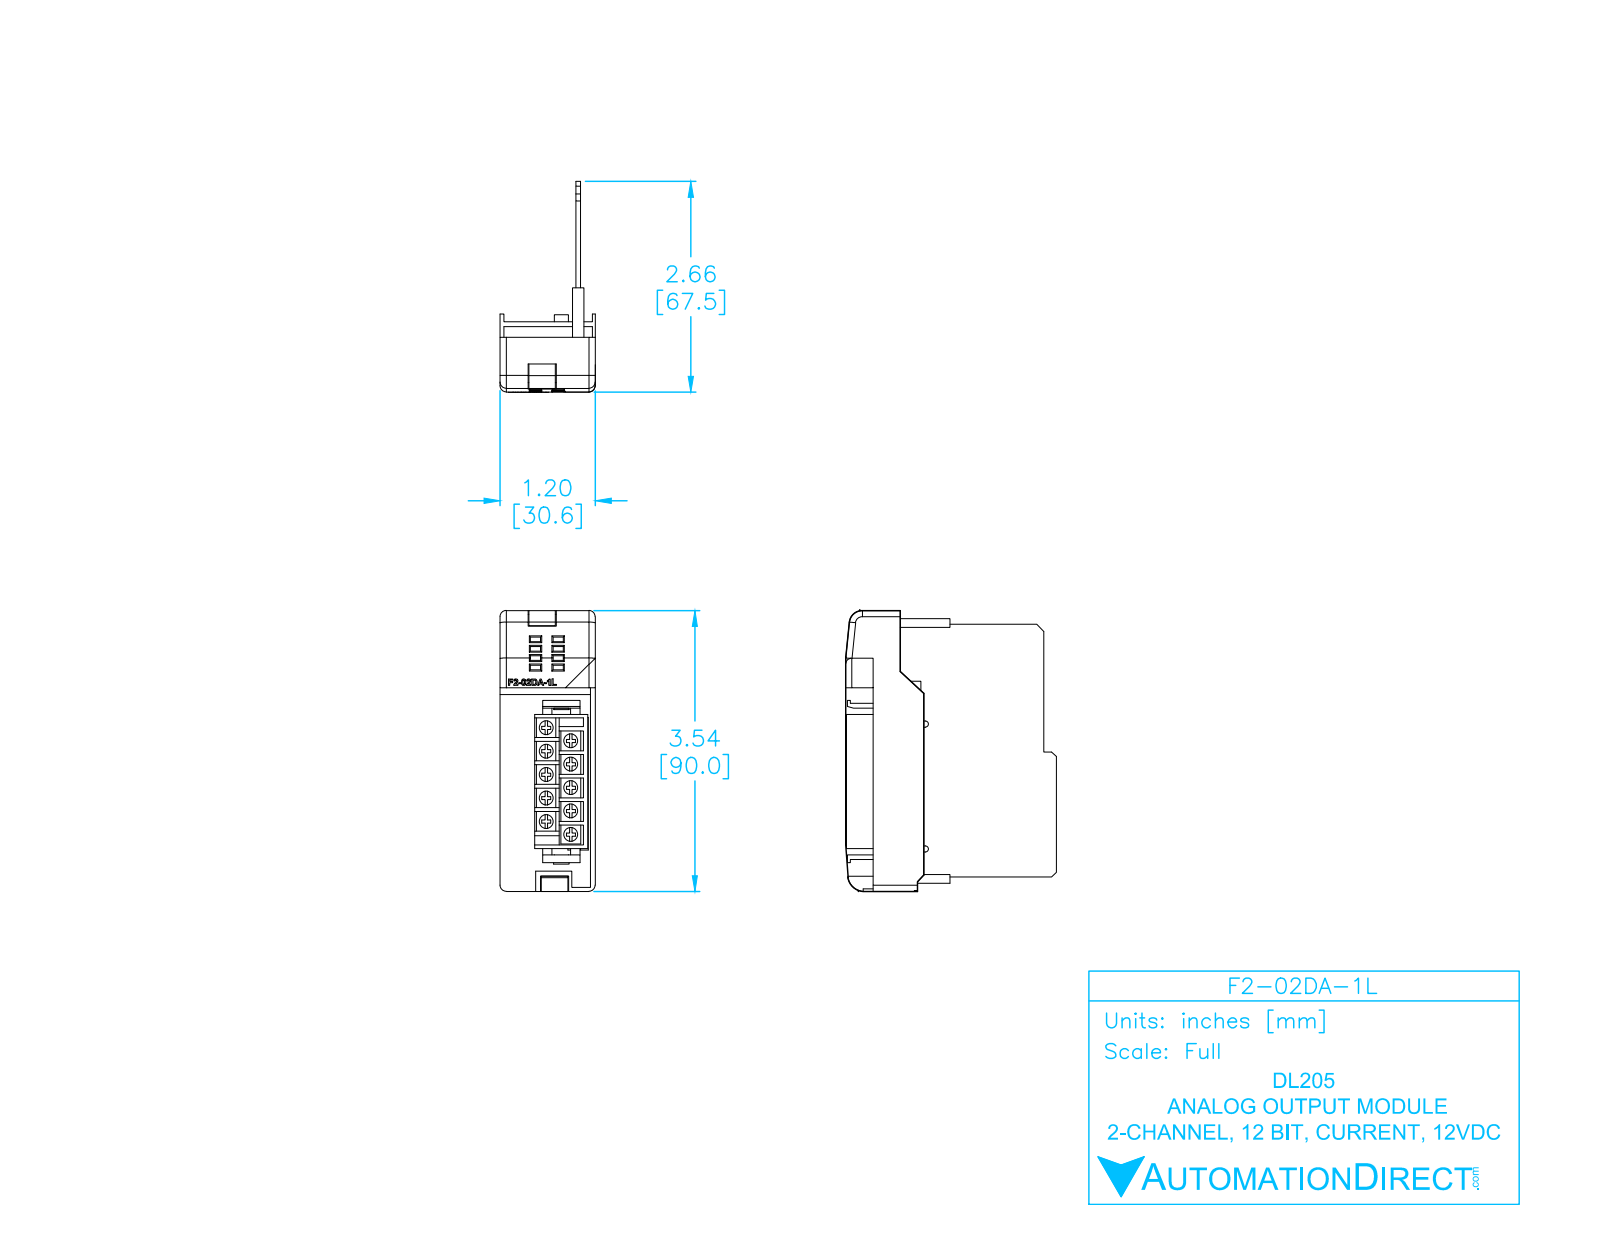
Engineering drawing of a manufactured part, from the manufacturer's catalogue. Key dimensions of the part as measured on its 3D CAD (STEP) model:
Part name (STEP PRODUCT): F2-02DA-1L_ModuleCase_light_NEW
STEP written by: SolidWorks 2009 (AUTOMOTIVE_DESIGN)
Units: millimetres
Bodies: 6 solids, 581 faces (421 planar, 75 cylindrical, 85 other)
Overall size (bounding box): 90 × 67.61 × 30.55
Volume: 25 374 mm³ · Surface area: 28 533 mm²
Round bosses / shafts (diameter × count): ⌀4.5 ×10
Partial cylindrical surfaces — rounded edges, fillets, slot ends (radius × count): R0.35 ×16, R2 ×9, R0.25 ×2, R1 ×2, R1.25 ×2, R4.12 ×1, R5.39 ×1
Main face-to-face distances: 1.5, 4.72, 6.22, 2.37, 3.87, 2.35, 3.22, 0.85, 8.14, 24.28
